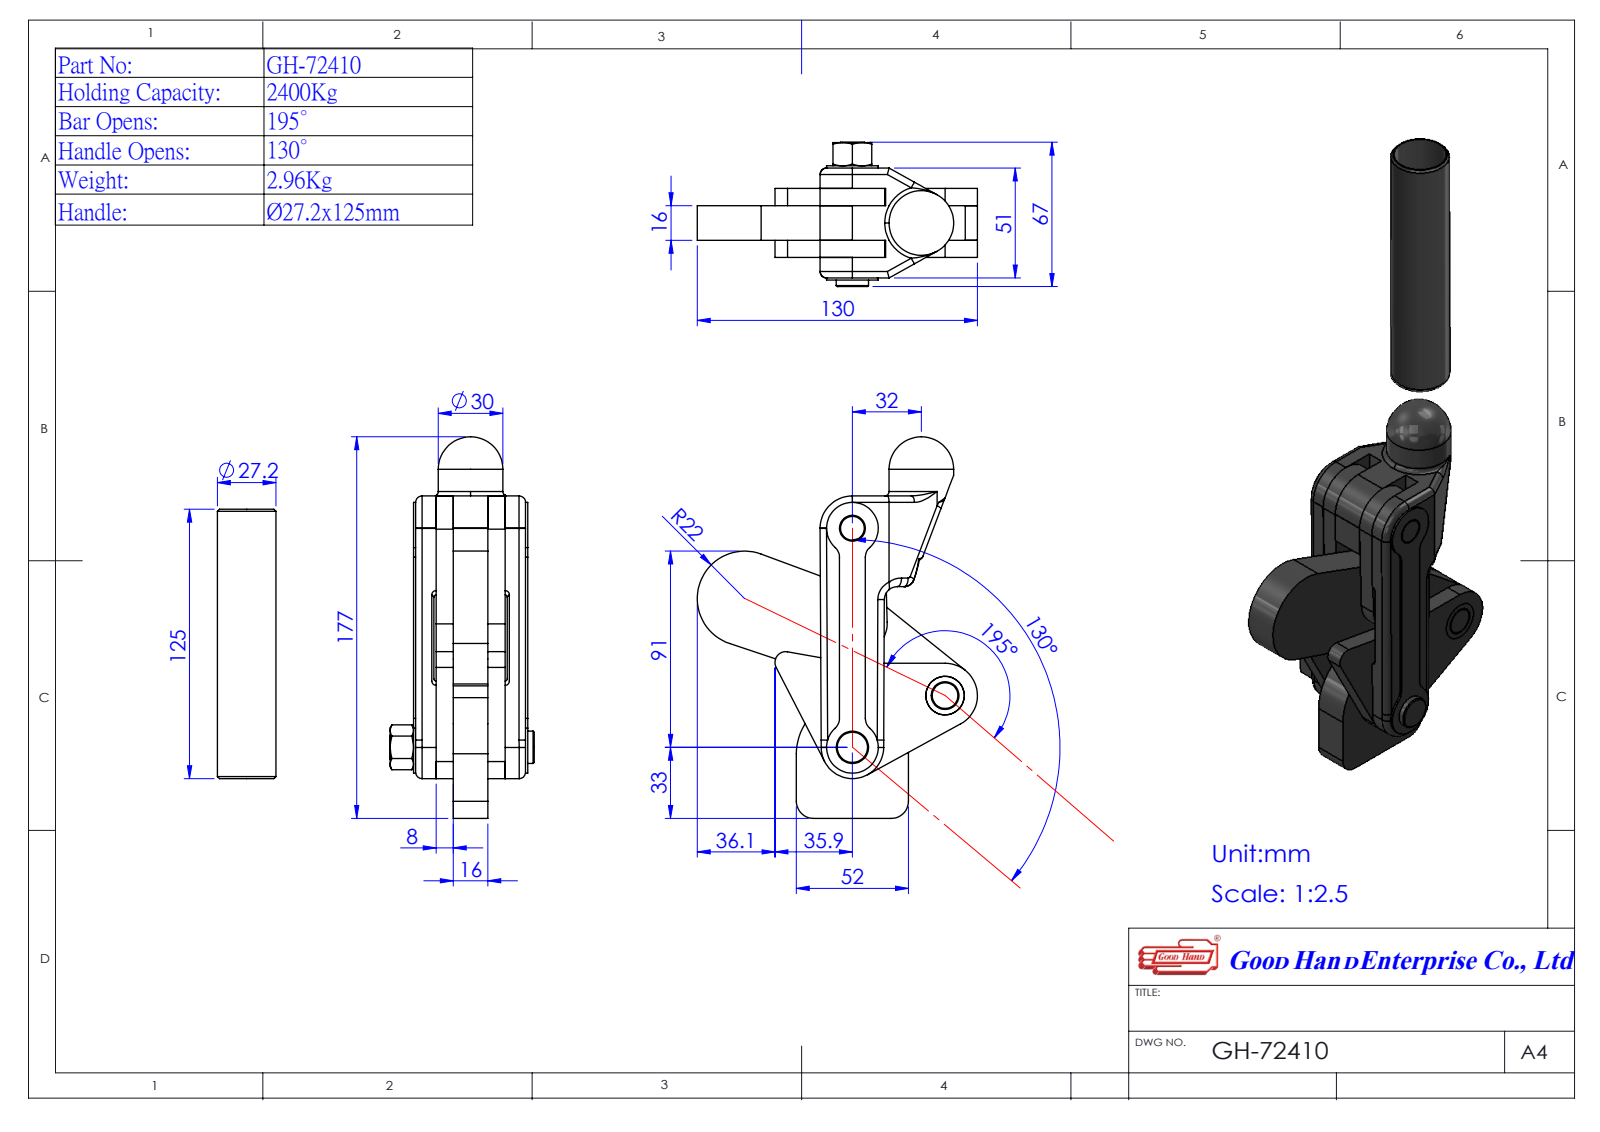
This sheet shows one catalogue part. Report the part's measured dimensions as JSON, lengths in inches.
{"part_name": "27241008-1^GH-72410(簡化); Group4^GH-72410(簡化); Group2^GH-72410(簡化); Group1^GH-72410(簡化) (+3 more)", "step_written_by": "SolidWorks 2016 (AUTOMOTIVE_DESIGN)", "units": "inches", "bodies": {"solids": 6, "faces": 178, "planar": 73, "cylindrical": 85, "other": 20}, "overall_size": [11.911, 5.118, 2.63], "volume_in3": 22.99, "surface_area_in2": 166.2, "round_holes": [[0.394, 4], [0.85, 1]], "round_bosses_or_shafts": [[1.181, 1], [1.071, 1], [0.591, 1]], "partial_cylinders_radius": [[0.236, 5], [0.591, 4], [0.197, 3], [0.118, 2], [0.315, 2], [0.472, 2], [0.571, 1], [0.866, 1]], "face_to_face_distances": [0.315, 0.945, 0.63, 1.26, 0.374, 0.689, 1.319, 1.634, 2.047, 0.039], "hole_center_spacings": [1.732, 1.939, 2.113, 2.269, 3.493, 4]}
